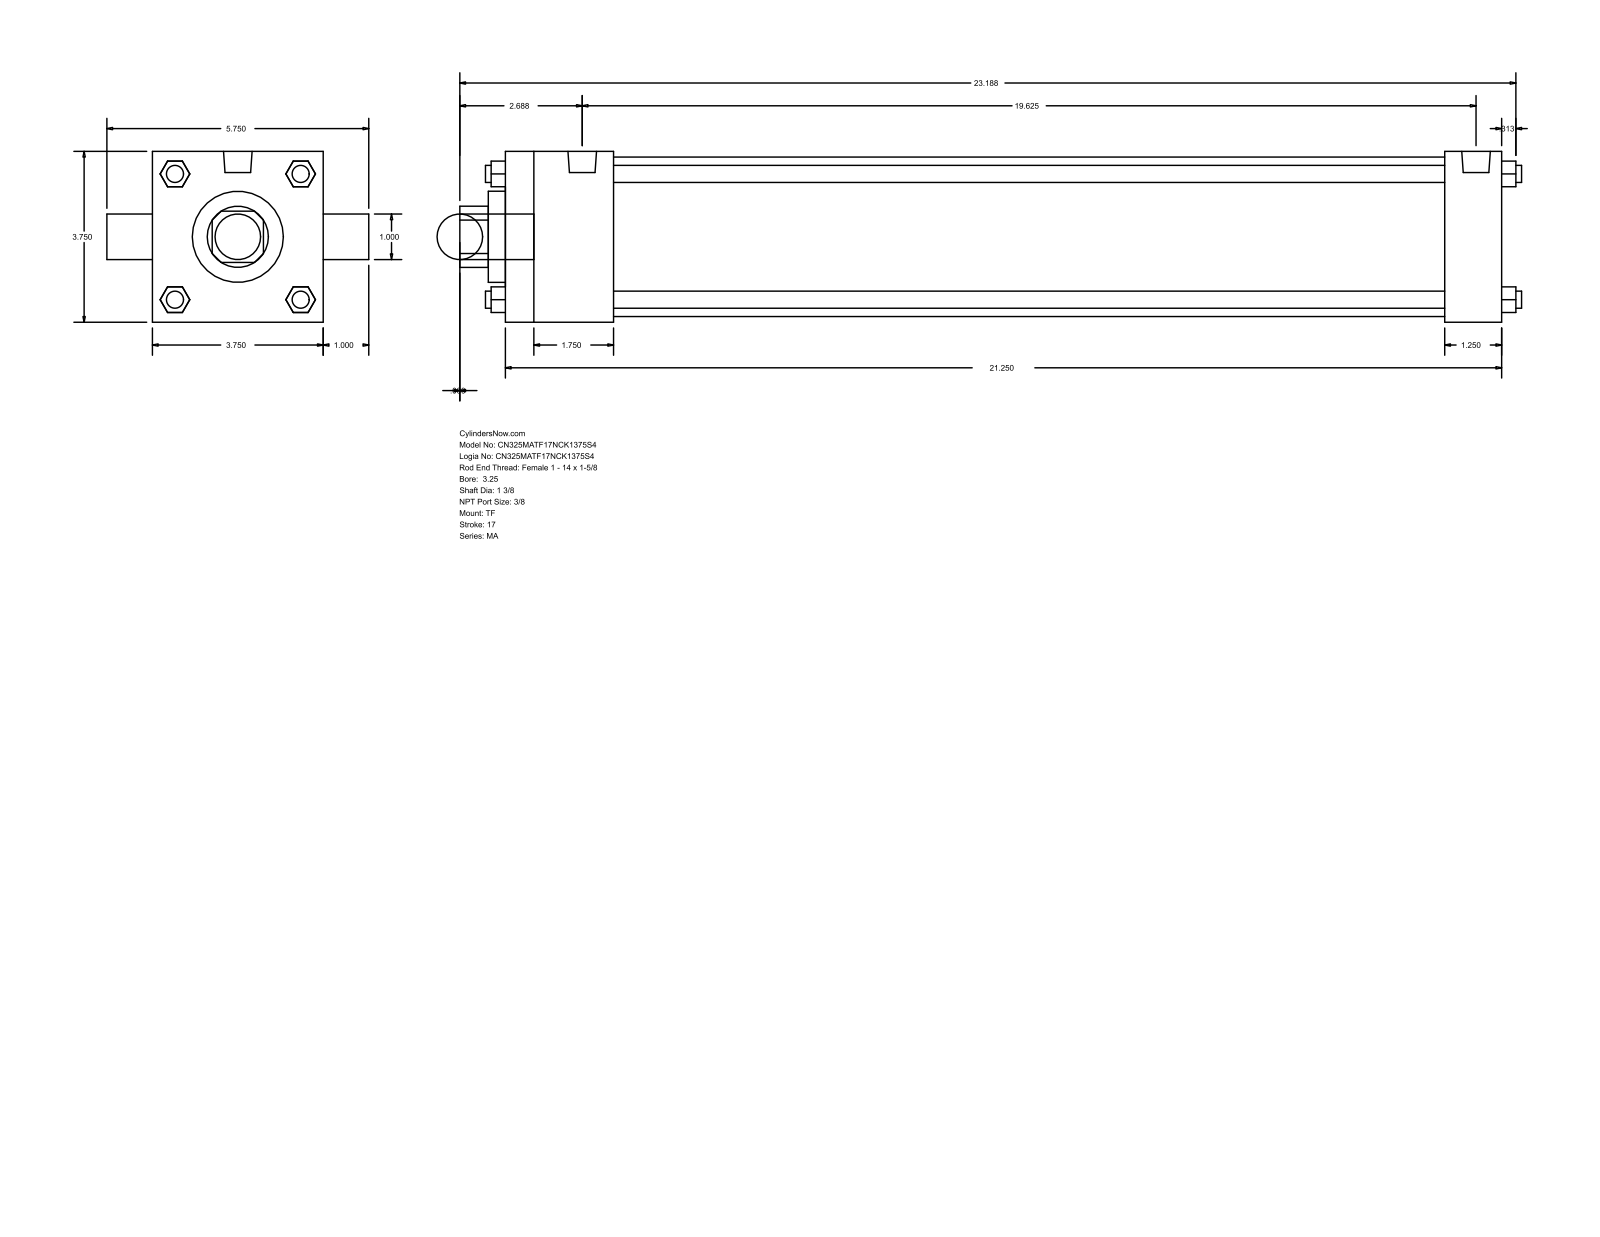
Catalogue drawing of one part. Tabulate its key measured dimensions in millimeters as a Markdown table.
| quantity | value |
| --- | --- |
| part name | MA_TF__0325_1.375 |
| STEP written by | GSSL Pune (CONFIG_CONTROL_DESIGN) |
| units | millimeters |
| bodies | 0 solids, 120 faces (92 planar, 28 cylindrical, 0 other) |
| overall size | 592.14 × 146.05 × 95.25 |
| round holes (diameter × count) | 25.4 × 1, 34.92 × 1, 50.8 × 1, 88.9 × 1 |
| round bosses / shafts (diameter × count) | 9.53 × 4, 11.11 × 3, 15.93 × 2, 25.4 × 1 |
| partial cylindrical surfaces (radius × count) | 17.06 × 1 |
| main face-to-face distances | 95.24, 555.62, 60.32, 523.87, 463.55, 495.3, 31.75, 9.52, 69.84, 533.39 |
